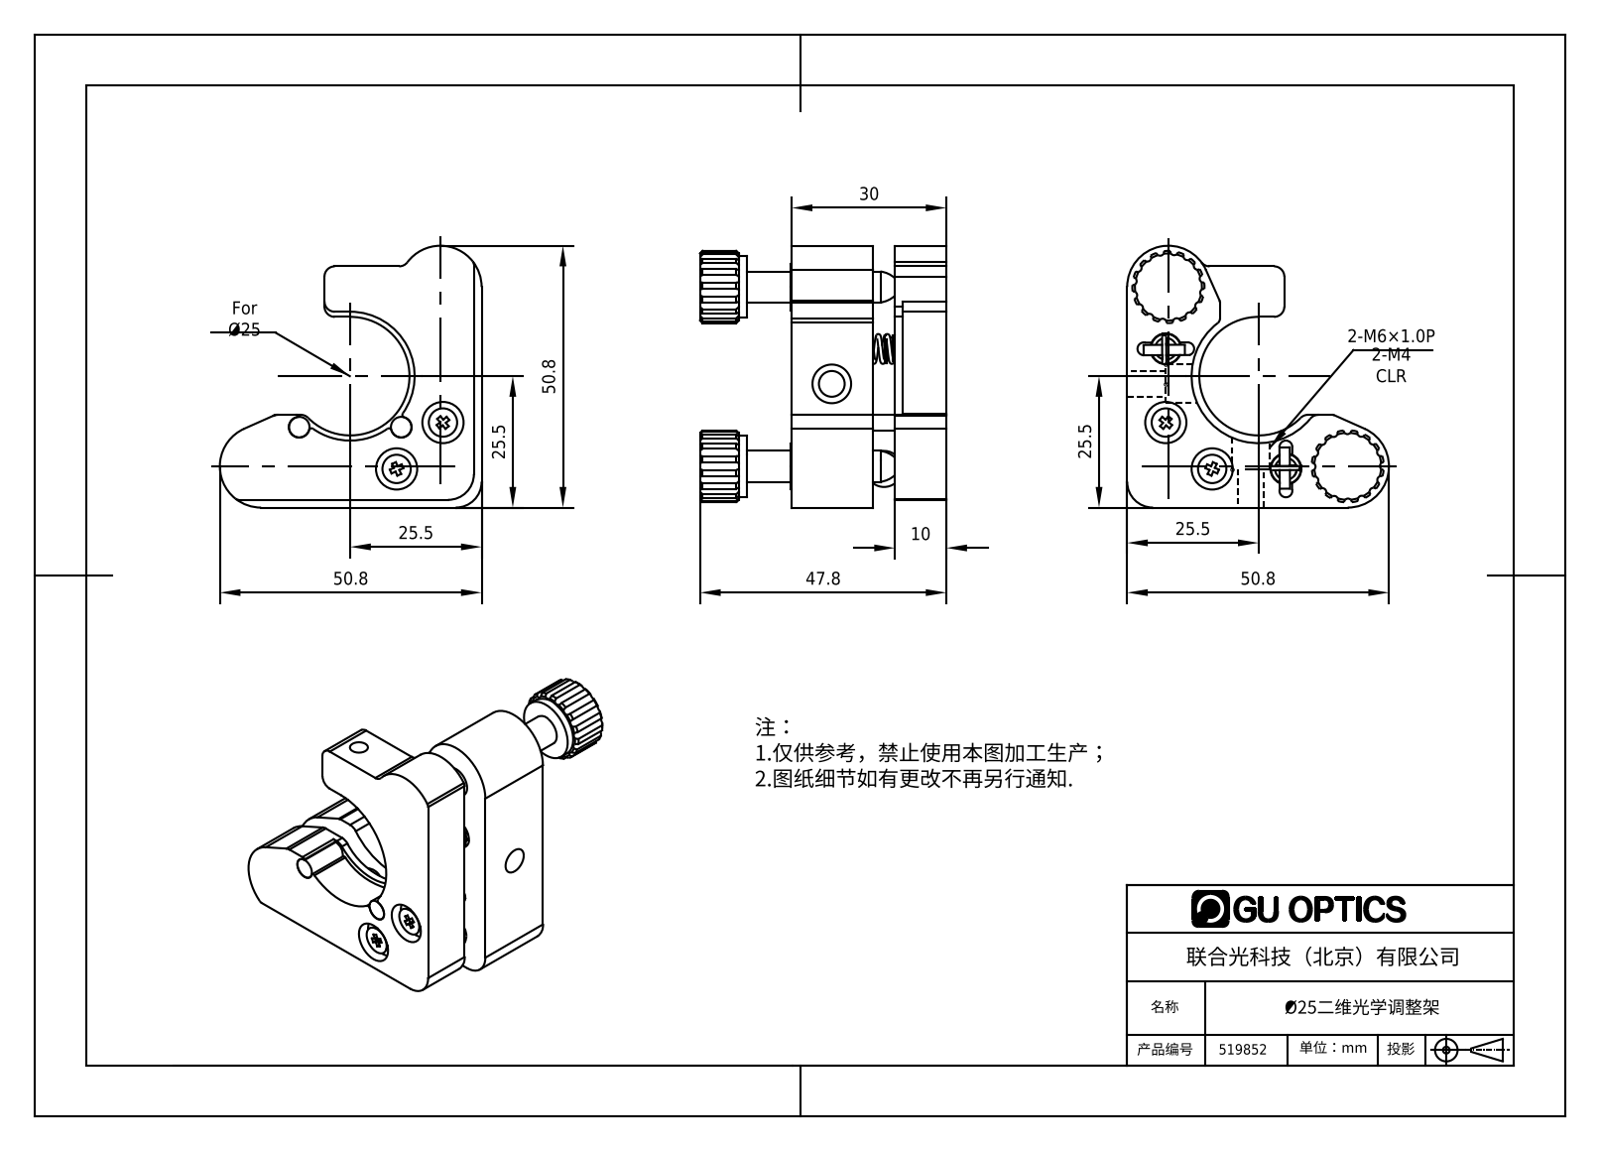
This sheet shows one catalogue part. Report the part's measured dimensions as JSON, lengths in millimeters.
{"part_name": "519852", "step_written_by": "SolidWorks 2016 (AUTOMOTIVE_DESIGN)", "units": "millimeters", "bodies": {"solids": 0, "faces": 628, "planar": 210, "cylindrical": 205, "other": 213}, "overall_size": [50.8, 50.8, 47.8], "round_holes": [[6, 4], [8, 4], [4, 3], [5, 2], [7.5, 2], [3.5, 1]], "round_bosses_or_shafts": [[12, 2], [9, 2], [5.4, 2], [3, 2], [2, 2], [0.8, 2], [4, 1]], "partial_cylinders_radius": [[0.75, 32], [2, 7], [1, 6], [1.25, 4], [0.5, 3], [5, 2], [7, 2], [8, 2]], "face_to_face_distances": [10, 4.2, 14.2, 20, 15.8, 30, 1.5, 37.8, 30.3, 17.8], "hole_center_spacings": [8.15, 12.01, 14.3, 17.22, 24.98, 26.3, 28.24, 36.31]}
